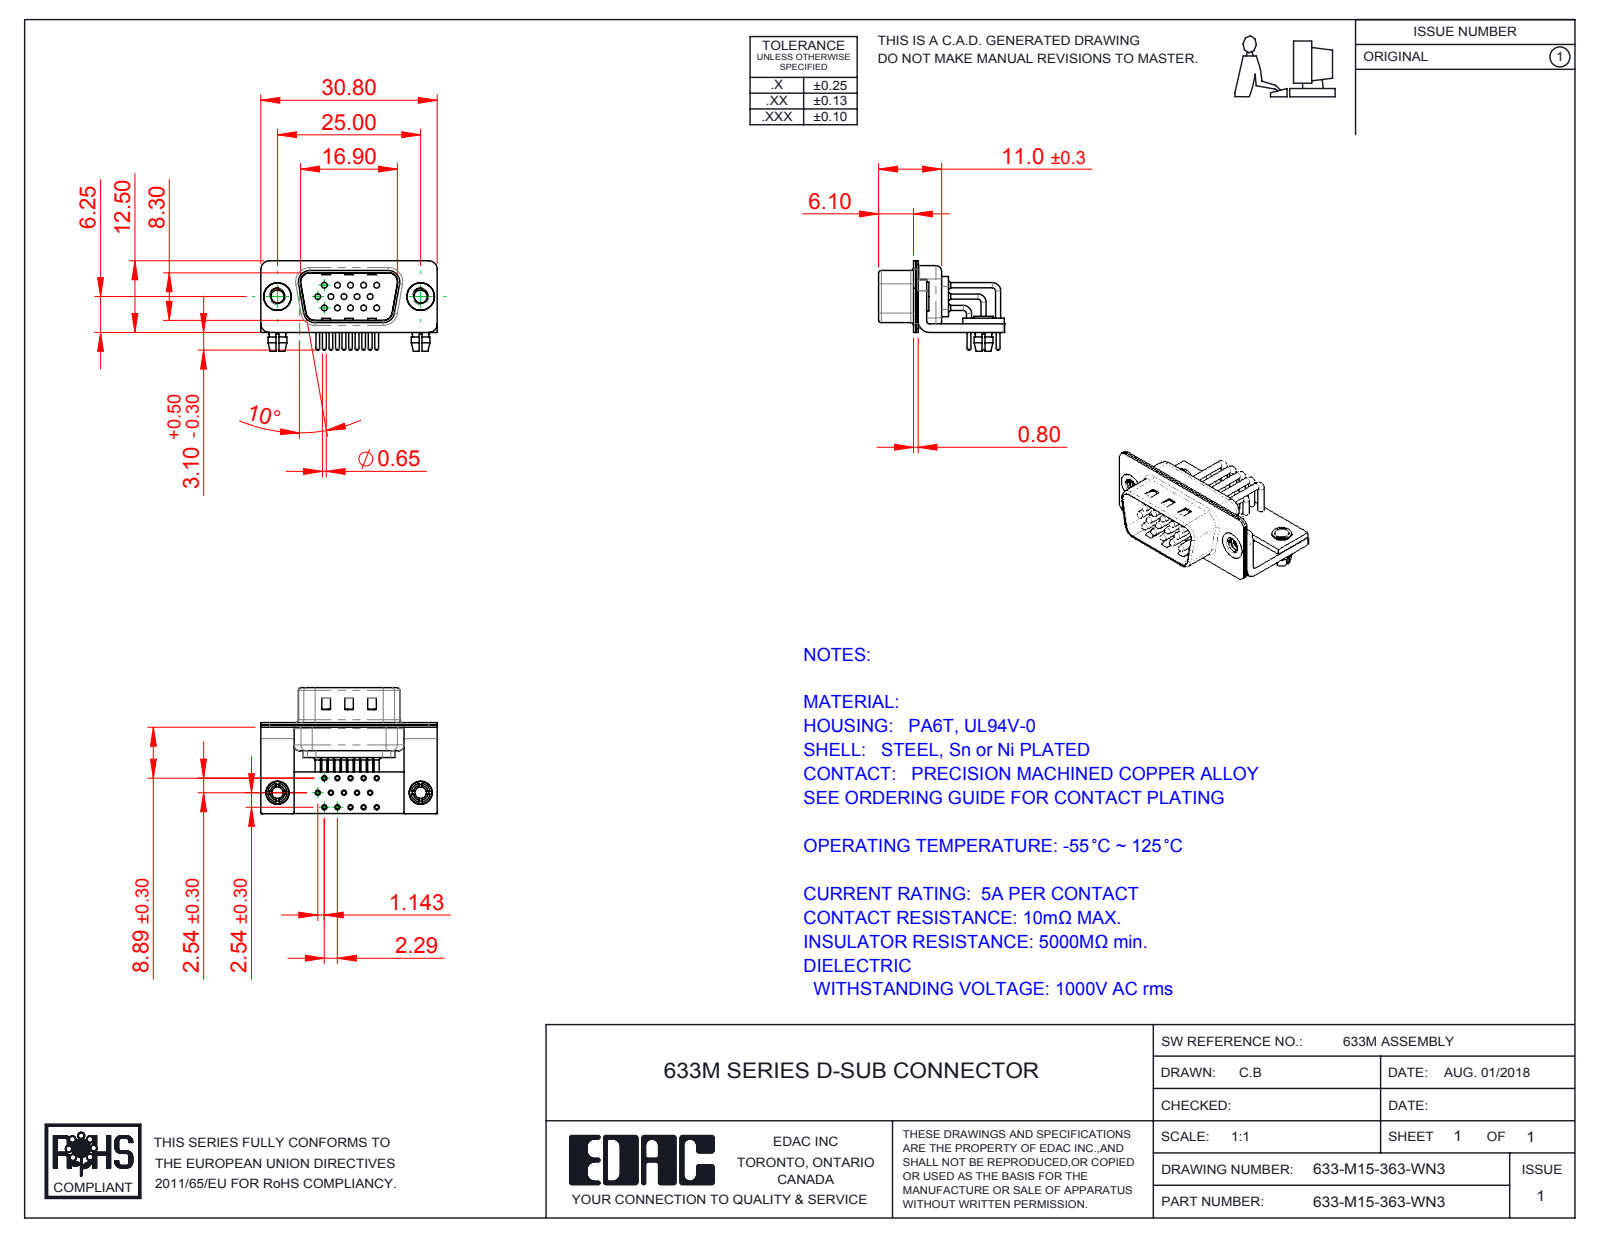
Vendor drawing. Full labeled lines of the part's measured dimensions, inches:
Part name (STEP PRODUCT): 633M Contact Row 2; 633M Shell Rear_15 Contacts; 633-M15-363-WN3; 633M Board Lock (+7 more)
STEP written by: SolidWorks 2016 (CONFIG_CONTROL_DESIGN)
Units: inches
Bodies: 25 solids, 2126 faces (1141 planar, 753 cylindrical, 232 other)
Overall size (bounding box): 1.213 × 0.866 × 0.622
Volume: 0.12 in³ · Surface area: 9.317 in²
Round holes (diameter × count): ⌀0.079 ×17, ⌀0.035 ×15, ⌀0.039 ×15, ⌀0.067 ×15, ⌀0.089 ×2, ⌀0.098 ×2, ⌀0.126 ×2, ⌀0.157 ×2, ⌀0.189 ×2
Round bosses / shafts (diameter × count): ⌀0.035 ×16, ⌀0.059 ×15, ⌀0.026 ×15, ⌀0.197 ×2, ⌀0.193 ×2, ⌀0.157 ×2, ⌀0.134 ×2, ⌀0.13 ×2
Partial cylindrical surfaces — rounded edges, fillets, slot ends (radius × count): R0.01 ×16, R0.059 ×16, R0.04 ×15, R0.079 ×13, R0.02 ×9, R0.063 ×8, R0.024 ×4, R0.026 ×4
Main face-to-face distances: 0.016, 0.059, 0.031, 0.039, 0.033, 0.075, 0.098, 0.049, 0.409, 0.376
Hole centre spacings: 0.09, 0.18, 0.09, 0.156, 0.109, 0.168, 0.238, 0.27
